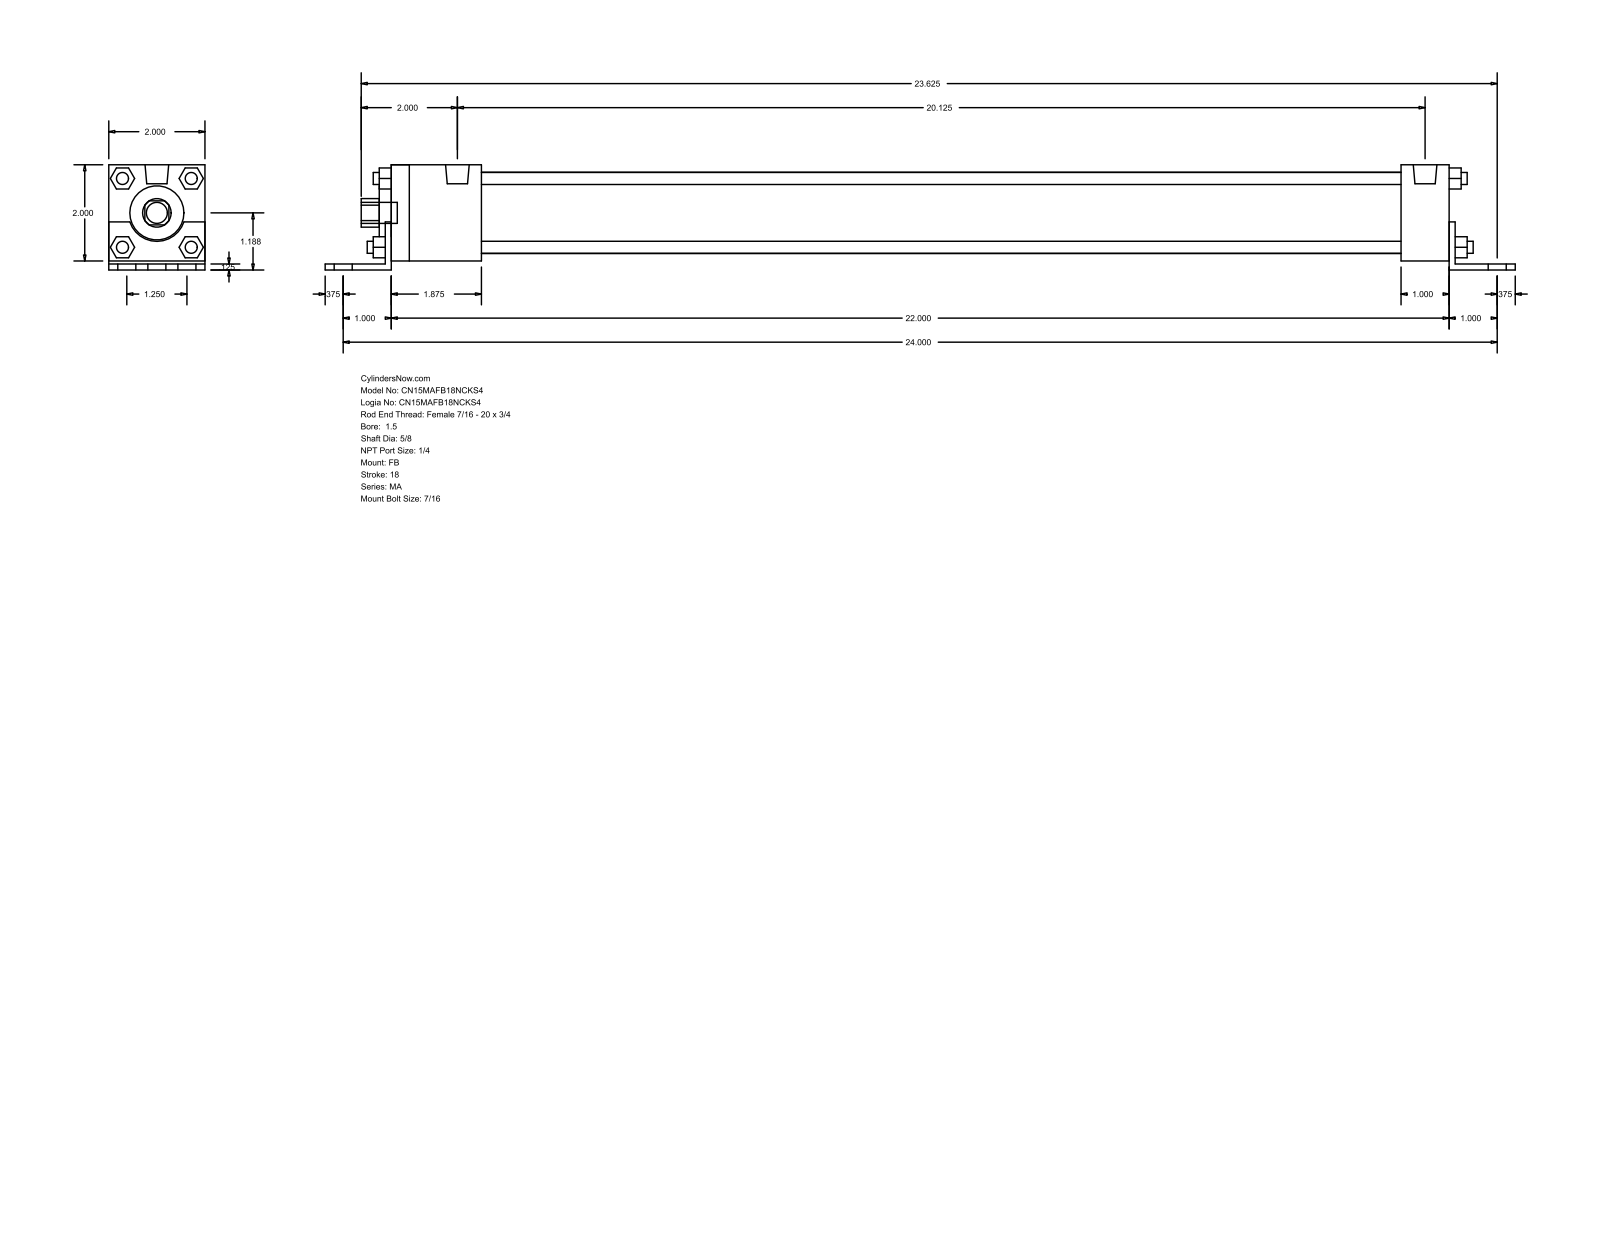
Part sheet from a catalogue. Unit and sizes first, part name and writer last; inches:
Units: inches
Overall size (bounding box): 24.75 × 2.187 × 2
Round holes (diameter × count): ⌀0.625 ×1, ⌀1.125 ×1, ⌀1.69 ×1
Round bosses / shafts (diameter × count): ⌀0.437 ×7, ⌀0.313 ×4, ⌀0.25 ×4, ⌀0.492 ×2
Partial cylindrical surfaces — rounded edges, fillets, slot ends (radius × count): R0.297 ×1, R0.593 ×1
Main face-to-face distances: 2, 0.125, 0.187, 2.187, 0.063, 2.063, 0.125, 22.125, 1, 22.375
Bodies: 0 solids, 140 faces (105 planar, 35 cylindrical, 0 other)
Part name (STEP PRODUCT): MA_FB__0150_0.625
STEP written by: GSSL Pune (CONFIG_CONTROL_DESIGN)
